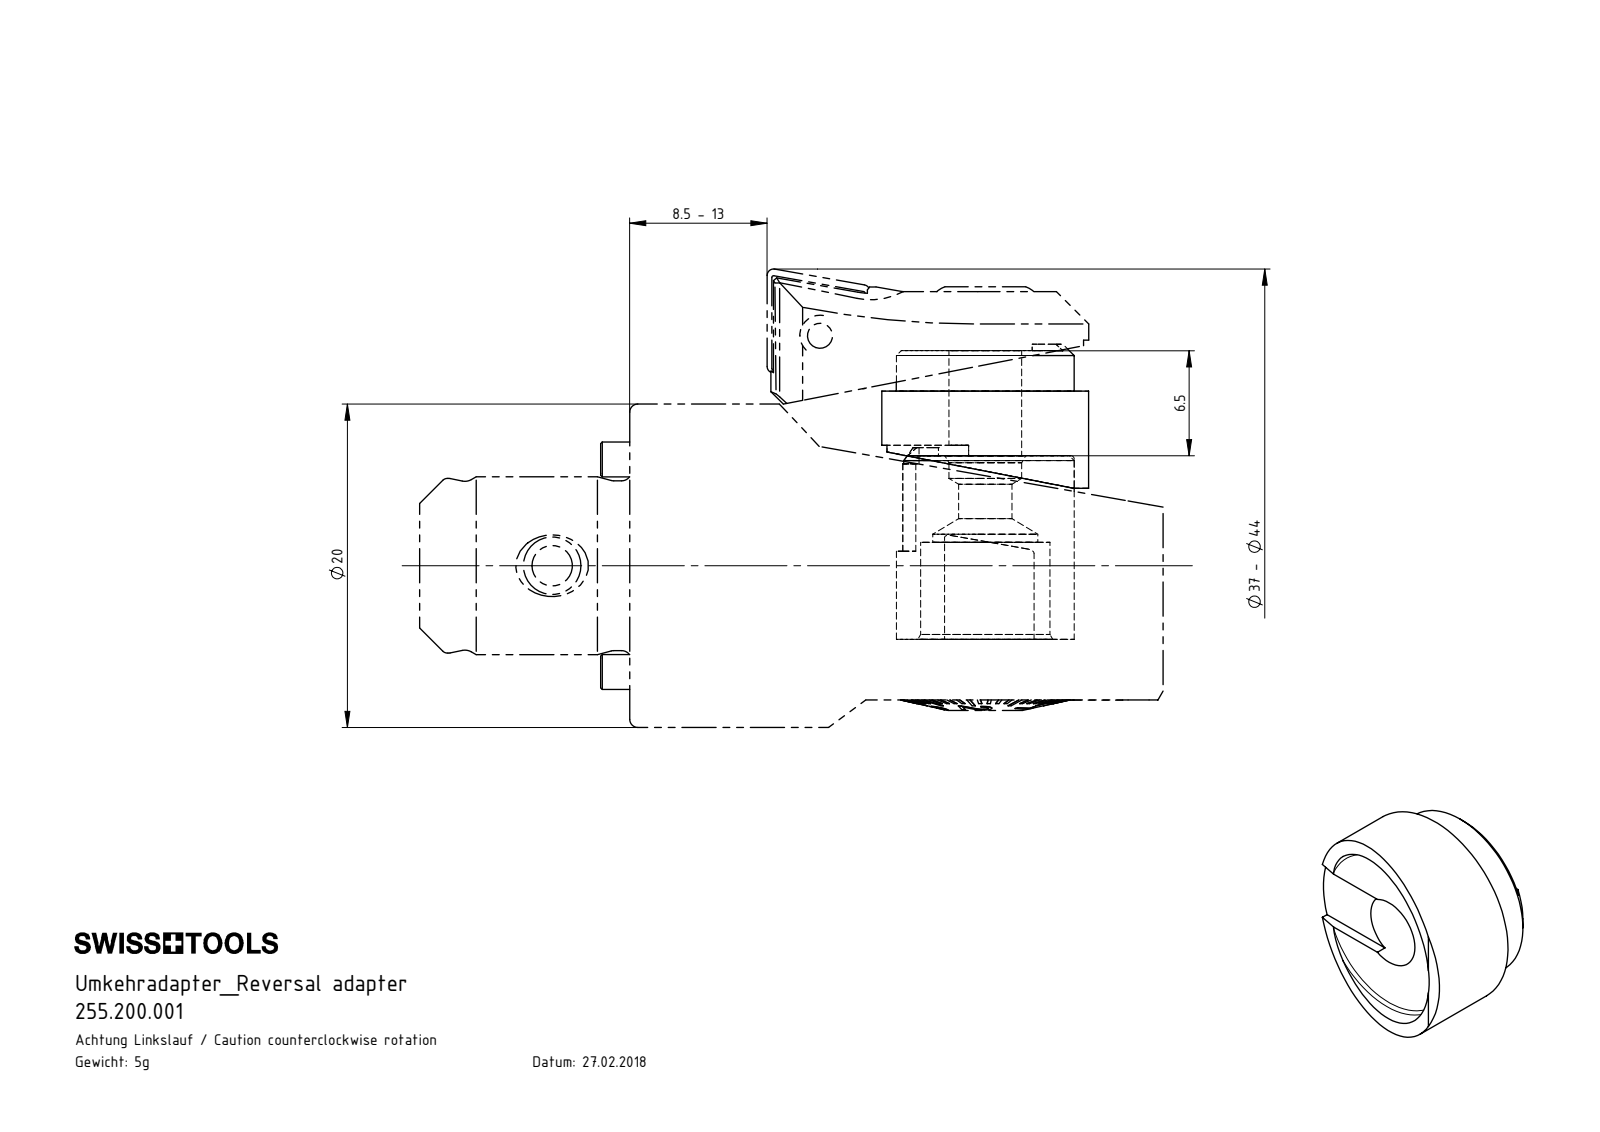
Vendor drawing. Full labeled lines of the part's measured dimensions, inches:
Part name (STEP PRODUCT): F20-U00.001.006_B; 255.200.001
STEP written by: SolidWorks 2017 (CONFIG_CONTROL_DESIGN)
Units: inches
Bodies: 1 solid, 29 faces (13 planar, 11 cylindrical, 5 other)
Overall size (bounding box): 0.504 × 0.504 × 0.35
Volume: 0.041 in³ · Surface area: 0.98 in²
Round holes (diameter × count): ⌀0.177 ×1, ⌀0.433 ×1
Round bosses / shafts (diameter × count): ⌀0.504 ×1
Partial cylindrical surfaces — rounded edges, fillets, slot ends (radius × count): R0.012 ×2
Main face-to-face distances: 0.256, 0.157, 0.098, 0.23, 0.132, 0.026, 0.016, 0.114, 0.246, 0.272
